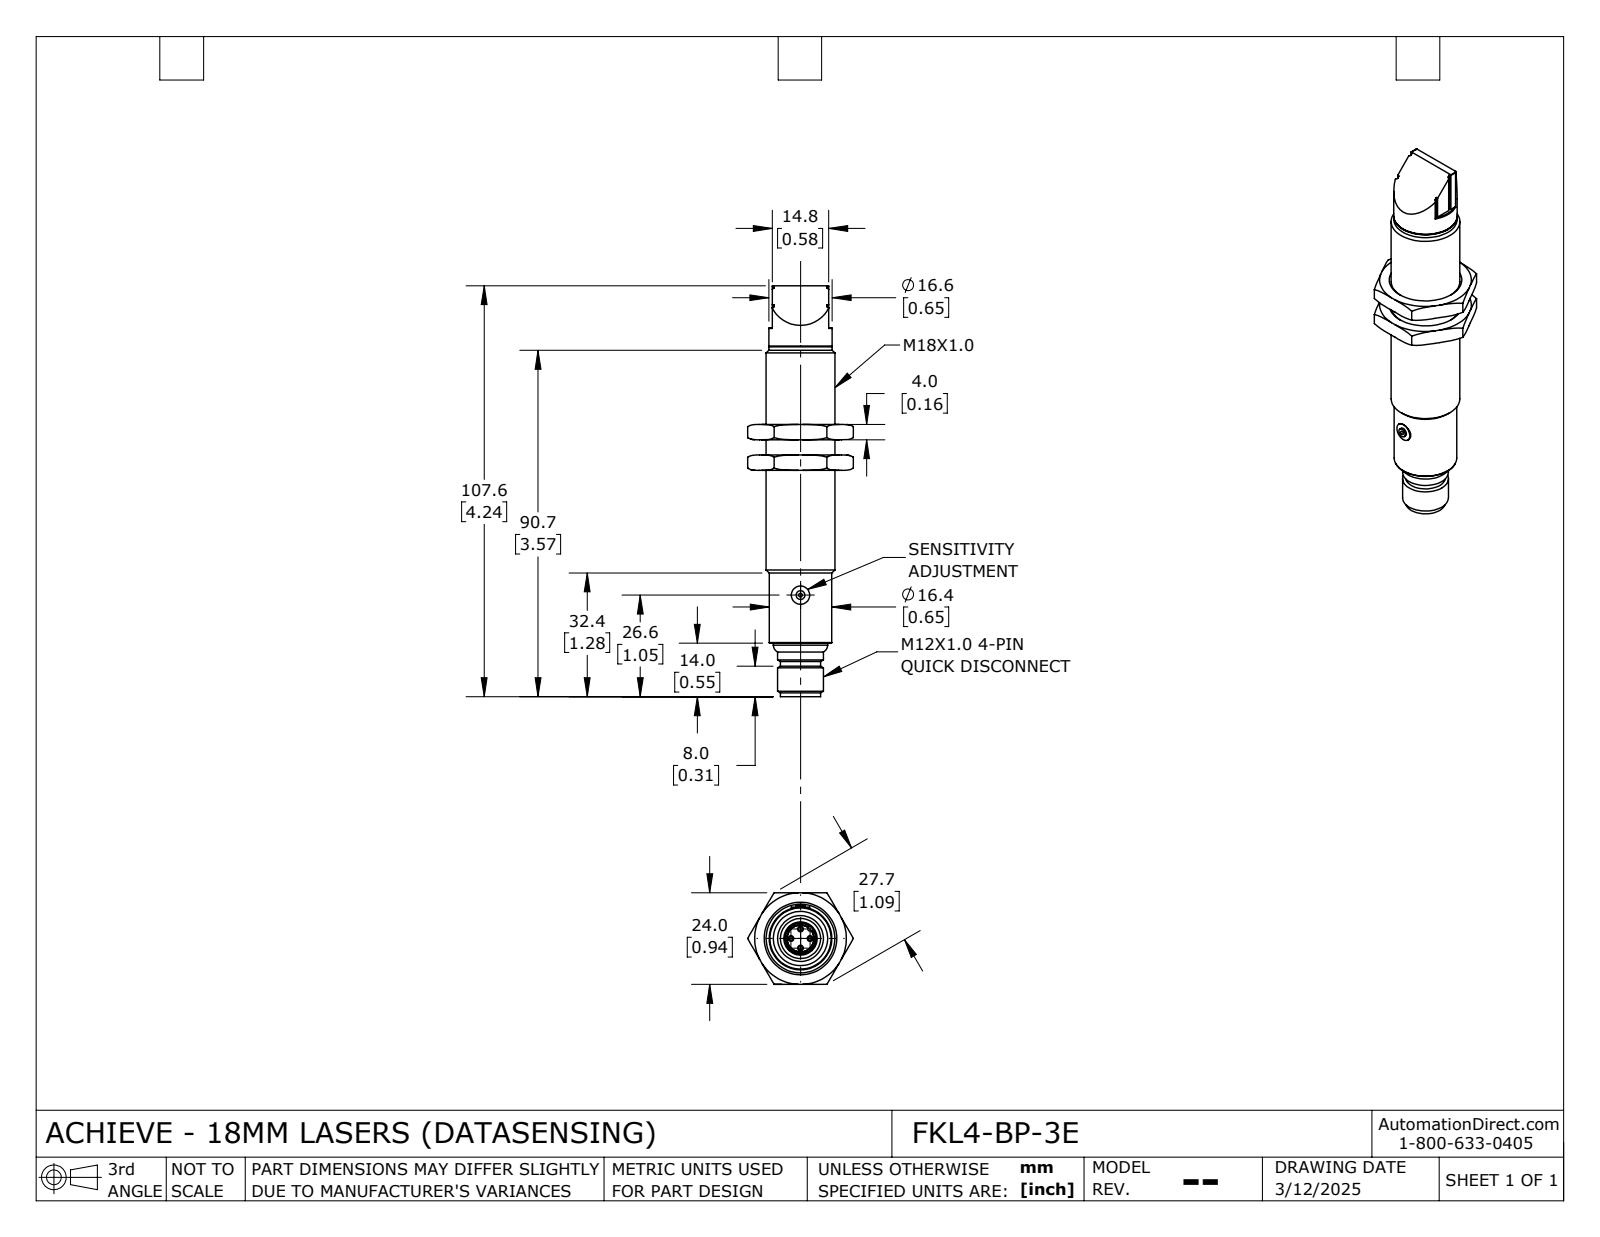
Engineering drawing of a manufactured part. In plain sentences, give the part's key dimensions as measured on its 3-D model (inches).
The part is named "FKL4-BP-3E_Default". Its 3-D file was written by "SolidWorks 2024 (CONFIG_CONTROL_DESIGN)". It is 3 solids with 146 faces: 64 planar, 30 cylindrical and 52 other. Overall it measures 4.236 by 1.091 by 0.945 inches. Its volume is 1.472 cubic inches and its surface area 14.05 square inches. Round holes: 1 of diameter 0.185, 1 of diameter 0.278, 1 of diameter 0.327, 1 of diameter 0.583, 1 of diameter 0.709. Round bosses or shafts: 4 of diameter 0.039, 1 of diameter 0.654, 1 of diameter 0.646, 1 of diameter 0.559, 1 of diameter 0.472, 1 of diameter 0.413, 1 of diameter 0.276, 1 of diameter 0.189. Partial cylindrical surfaces (rounded edges, fillets, slot ends): 2 of radius 0.004, 2 of radius 0.02, 1 of radius 0.024, 1 of radius 0.297. The main face-to-face distances are 0.157, 0.315, 0.945, 1.253, 1.261, 0.938, 0.946, 0.472, 1.41, 1.418.
